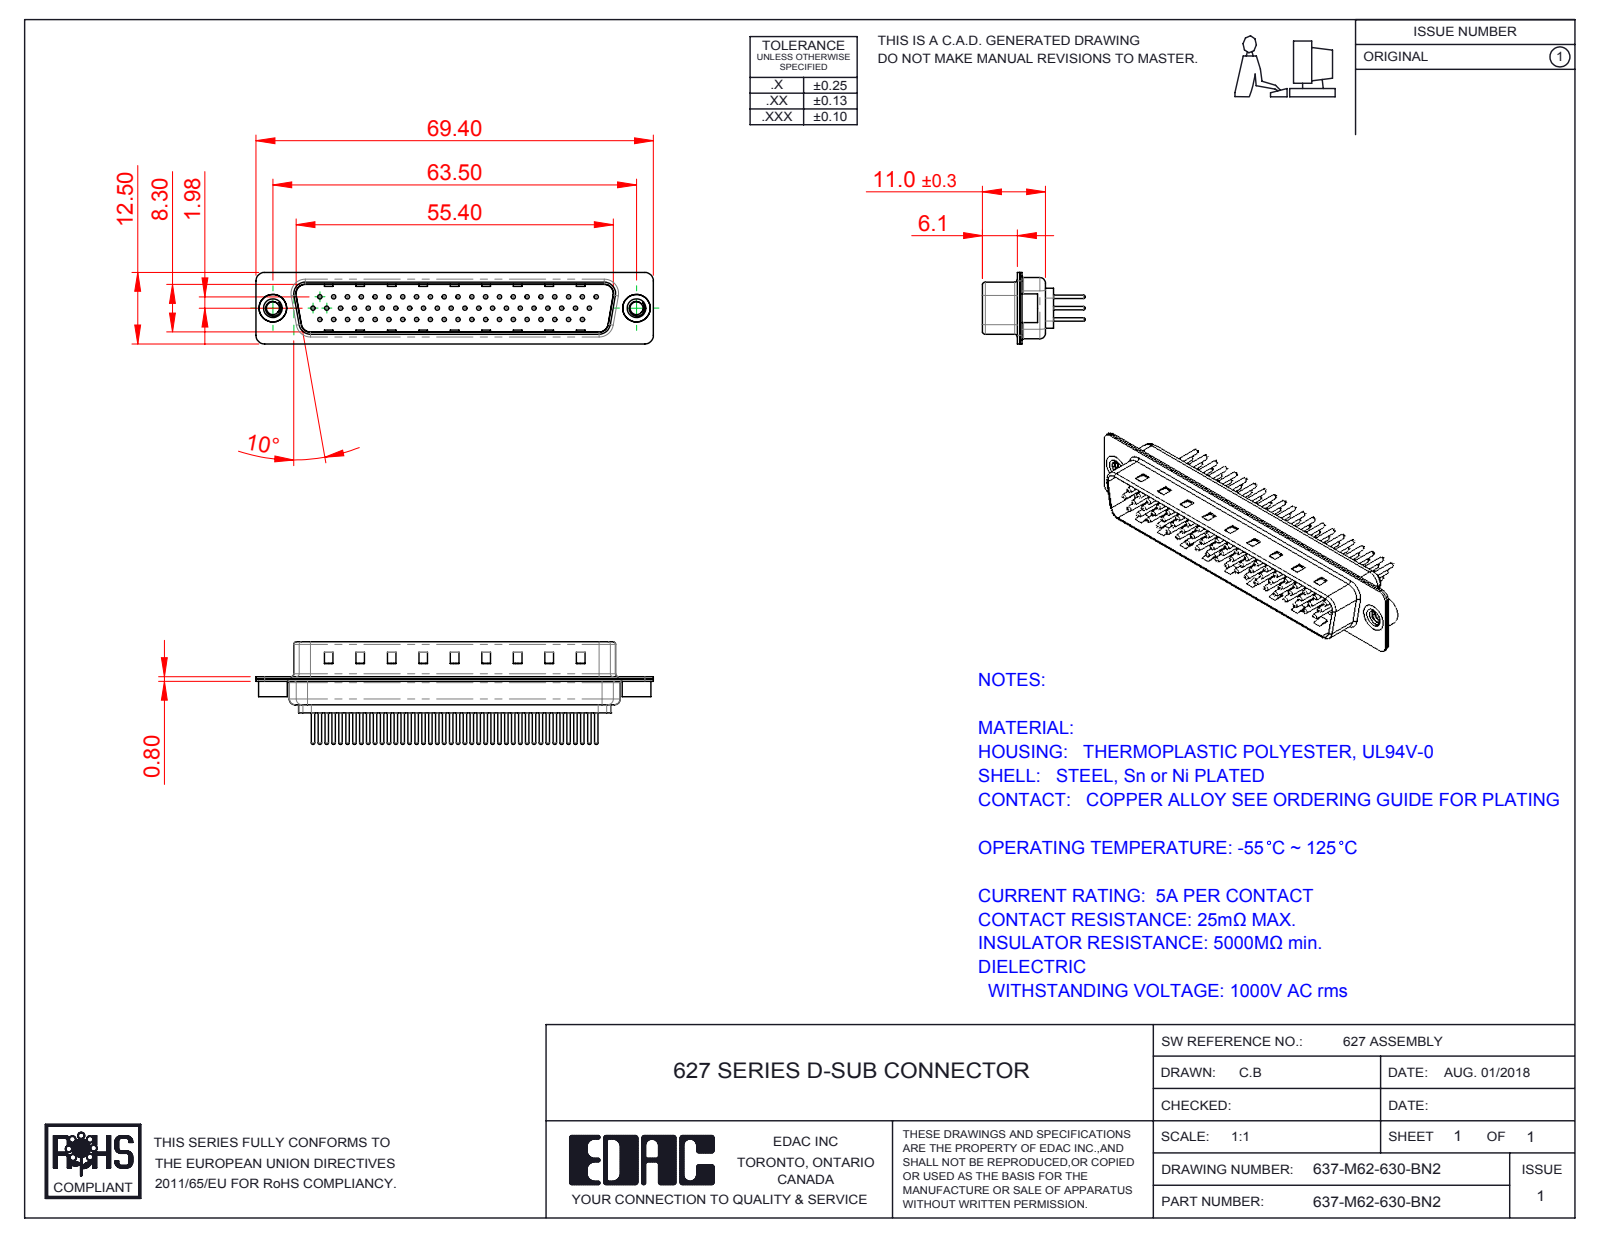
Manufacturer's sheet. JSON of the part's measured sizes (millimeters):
{"part_name": "637M Contact Row 1_30; 637M 4-40 Threaded Rivet; 637M Shell Front_62 Contacts; 637M Contact Row 3_30 (+4 more)", "step_written_by": "SolidWorks 2016 (CONFIG_CONTROL_DESIGN)", "units": "millimeters", "bodies": {"solids": 67, "faces": 2706, "planar": 637, "cylindrical": 1009, "other": 1060}, "overall_size": [69.4, 17.9, 12.5], "volume_mm3": 3918, "surface_area_mm2": 11413, "round_holes": [[0.75, 62], [1.6, 62], [2, 62], [2.26, 2], [4, 2], [4.8, 2]], "round_bosses_or_shafts": [[1.5, 62], [0.6, 62], [5, 2], [4.9, 2]], "partial_cylinders_radius": [[1.5, 16], [2, 12], [0.5, 8], [1.6, 8], [0.25, 4], [0.6, 4], [0.65, 4], [0.9, 4]], "face_to_face_distances": [0.4, 0.8, 9.5, 9.1, 8.7, 9.9, 0.75, 0.35, 5.9, 1.2], "hole_center_spacings": [7.24, 2.32, 2.41, 4.13, 9.65, 4.83, 14.48, 11.04]}
